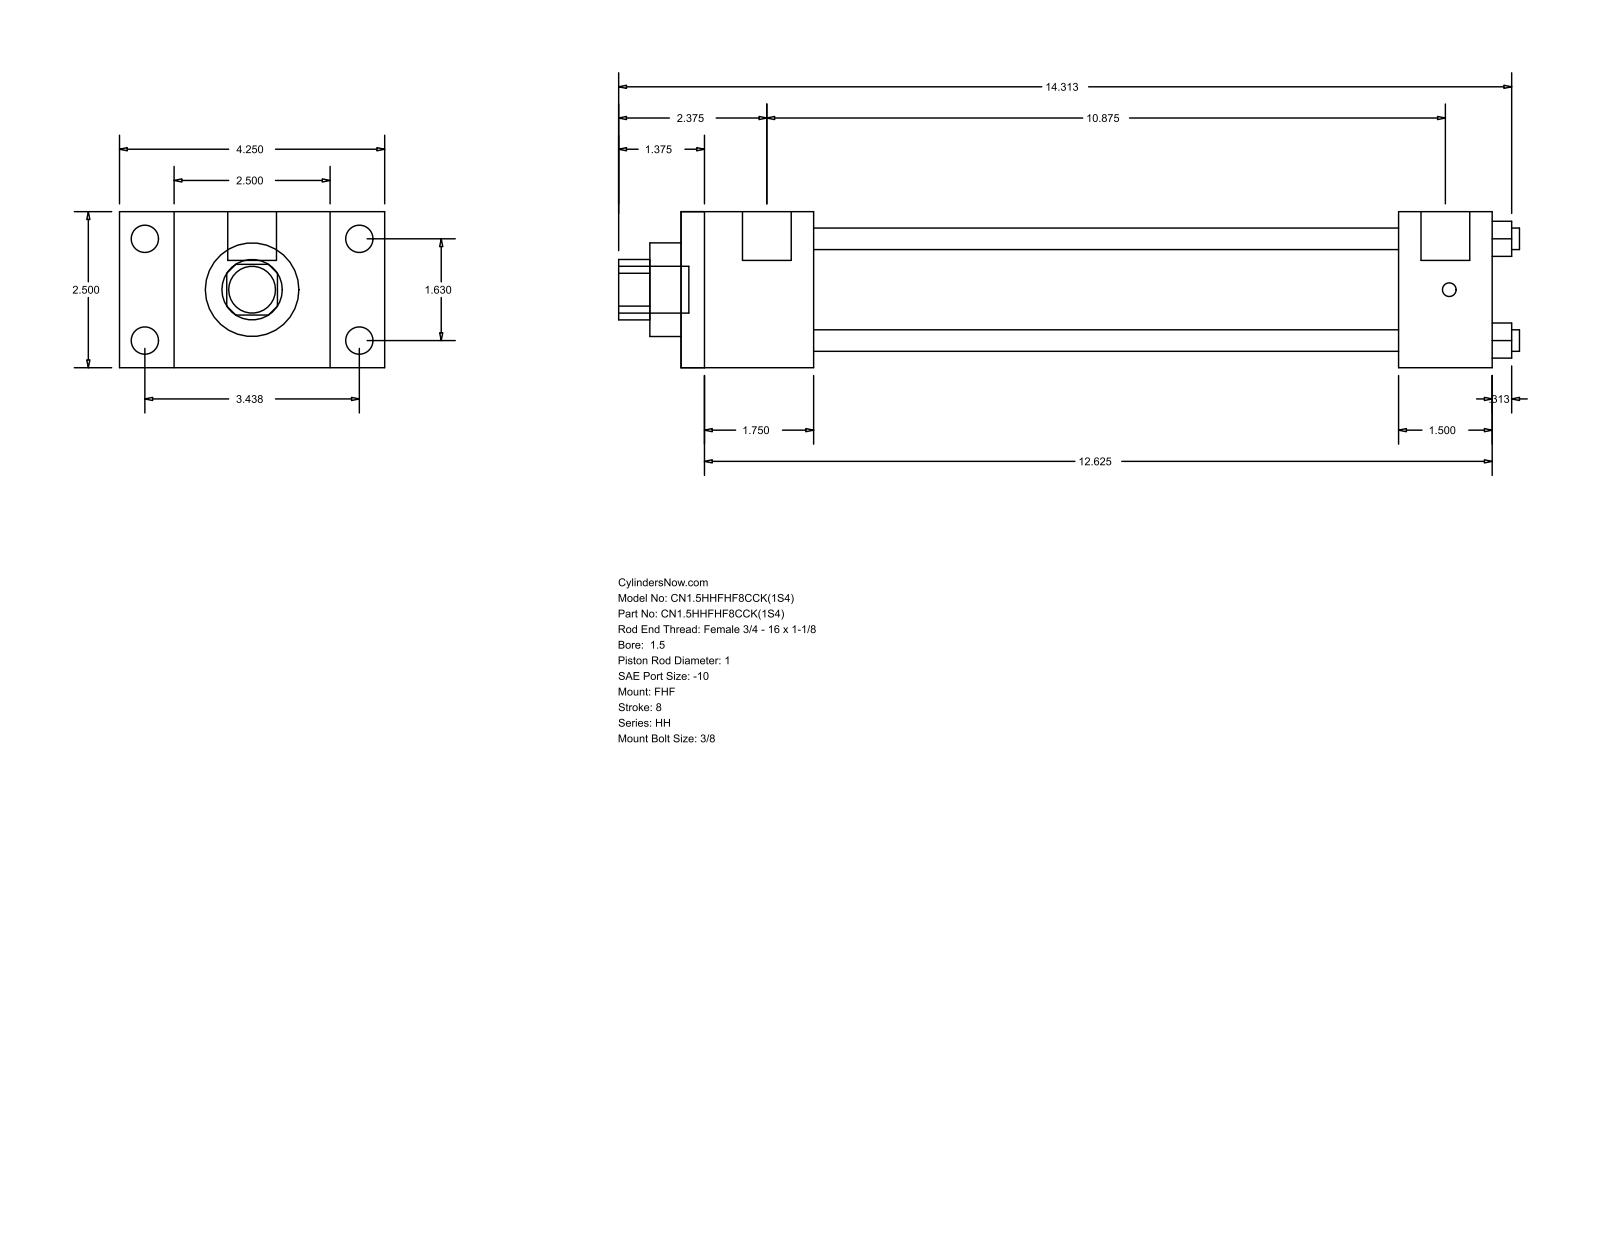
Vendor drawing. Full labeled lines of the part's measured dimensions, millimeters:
Part name (STEP PRODUCT): HH_FHF__0150_1
STEP written by: GSSL Pune (CONFIG_CONTROL_DESIGN)
Units: millimetres
Bodies: 0 solids, 88 faces (60 planar, 28 cylindrical, 0 other)
Overall size (bounding box): 366.71 × 107.95 × 63.5
Round holes (diameter × count): ⌀8.76 ×4, ⌀25.4 ×1, ⌀38.1 ×1, ⌀44.45 ×1
Round bosses / shafts (diameter × count): ⌀11.13 ×4, ⌀5.56 ×4, ⌀19.84 ×2, ⌀19.05 ×1
Partial cylindrical surfaces — rounded edges, fillets, slot ends (radius × count): R12.29 ×1
Main face-to-face distances: 63.5, 22.23, 85.73, 53.98, 107.96, 330.2, 276.22, 292.1, 238.12, 38.1
Hole centre spacings: 29.27, 41.4, 58.55
